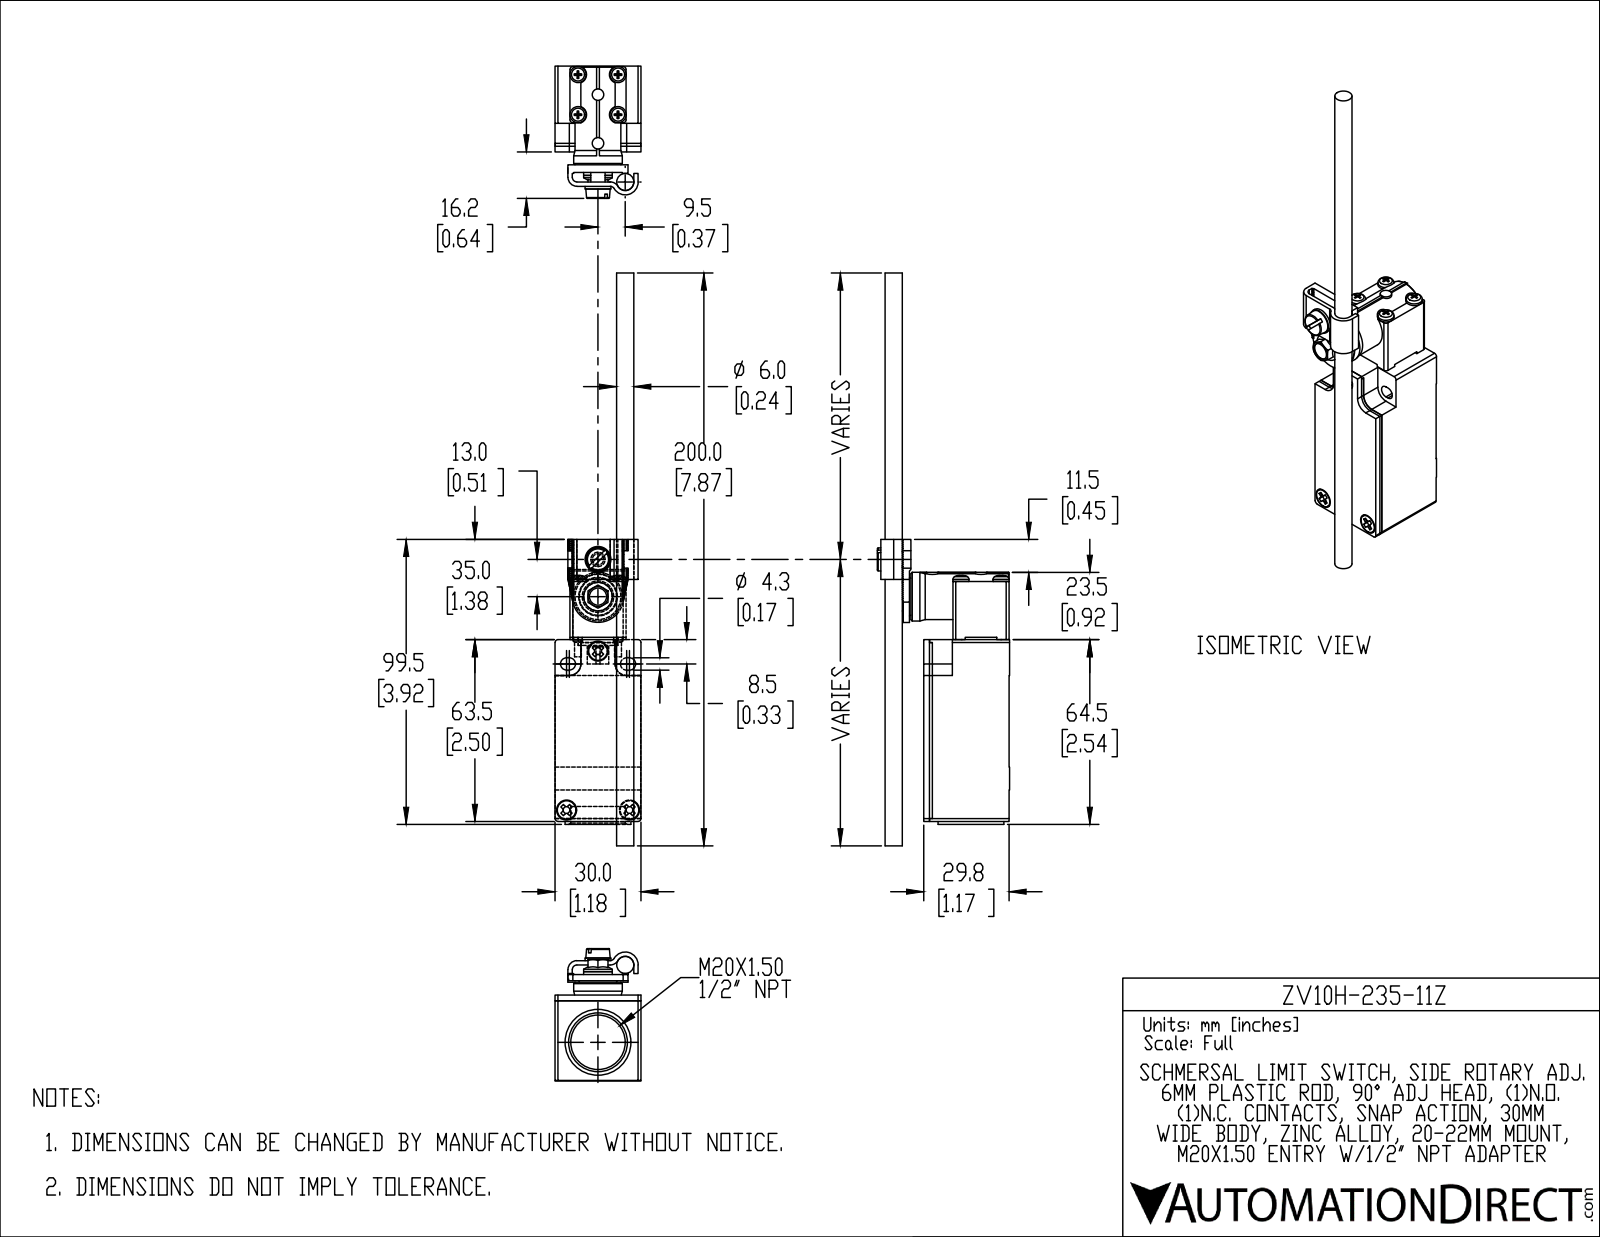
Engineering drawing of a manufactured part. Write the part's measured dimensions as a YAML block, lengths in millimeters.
part_name: "ZV10H-235-11Z"
step_written_by: "SolidWorks 2019 (AUTOMOTIVE_DESIGN)"
units: millimeters
bodies: {solids: 2, faces: 593, planar: 477, cylindrical: 91, other: 25}
overall_size: [200, 46.2, 30]
volume: 71630
surface_area: 20810
round_holes:
  - {diameter: 2.4, count: 4}
  - {diameter: 3.2, count: 4}
  - {diameter: 7, count: 3}
  - {diameter: 6, count: 2}
  - {diameter: 3.9, count: 1}
  - {diameter: 13, count: 1}
  - {diameter: 13.8, count: 1}
  - {diameter: 19, count: 1}
round_bosses_or_shafts:
  - {diameter: 5.6, count: 4}
  - {diameter: 5.4, count: 4}
  - {diameter: 6.5, count: 3}
  - {diameter: 10, count: 2}
  - {diameter: 4, count: 2}
  - {diameter: 23, count: 1}
  - {diameter: 17, count: 1}
  - {diameter: 16, count: 1}
partial_cylinders:
  - {radius: 0.5, count: 12}
  - {radius: 1, count: 8}
  - {radius: 1.5, count: 4}
  - {radius: 2.2, count: 4}
  - {radius: 3, count: 4}
  - {radius: 1.6, count: 2}
  - {radius: 3.1, count: 2}
  - {radius: 4, count: 2}
face_to_face_distances: [30, 29.8, 5.2, 24.8, 19.6, 4.5, 63.5, 7.1, 37, 37.2]
hole_center_spacings: [9.9, 14, 7.8, 12.6, 19.8, 56.6, 75.3, 88.2]
